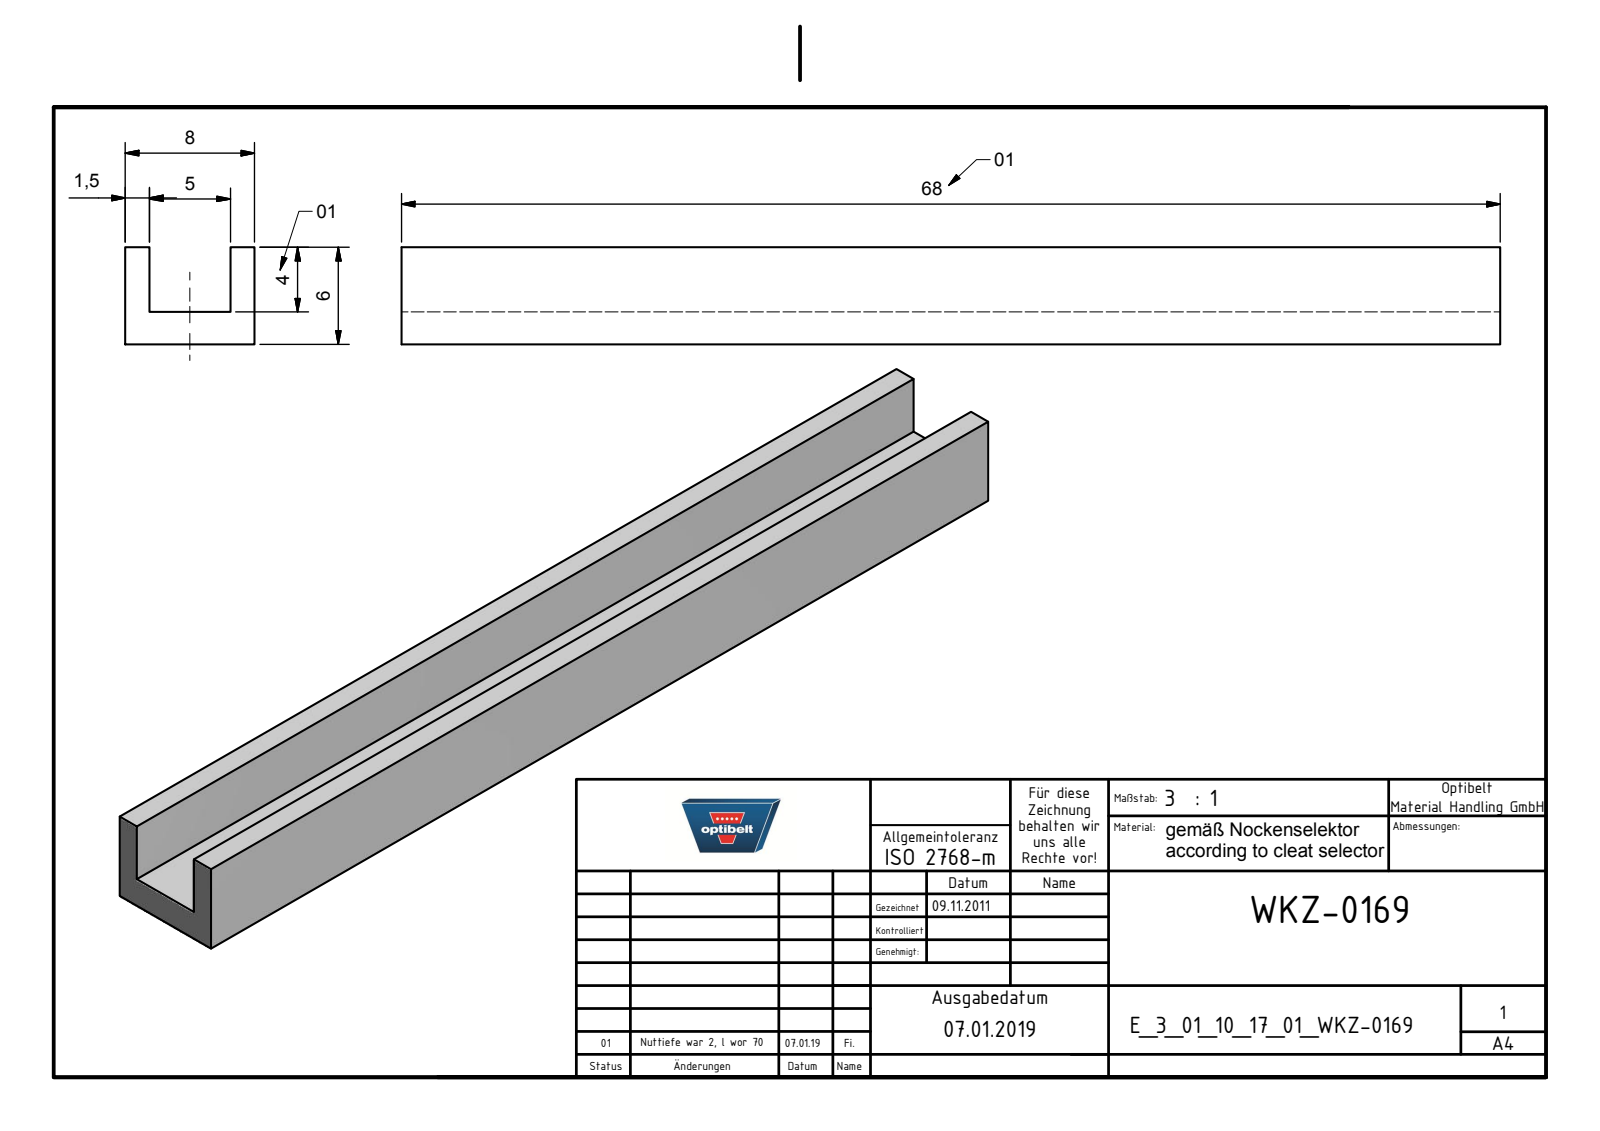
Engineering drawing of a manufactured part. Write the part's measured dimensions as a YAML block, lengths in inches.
part_name: "E_3_01_10_17_01_WKZ-0169"
step_written_by: "Autodesk Inventor 2025 (AUTOMOTIVE_DESIGN)"
units: inches
bodies: {solids: 1, faces: 10, planar: 10, cylindrical: 0, other: 0}
overall_size: [2.677, 0.315, 0.236]
volume: 0.116
surface_area: 3.881
face_to_face_distances: [0.059, 0.256, 0.315, 0.079, 0.197, 0.236, 0.157, 2.677]
